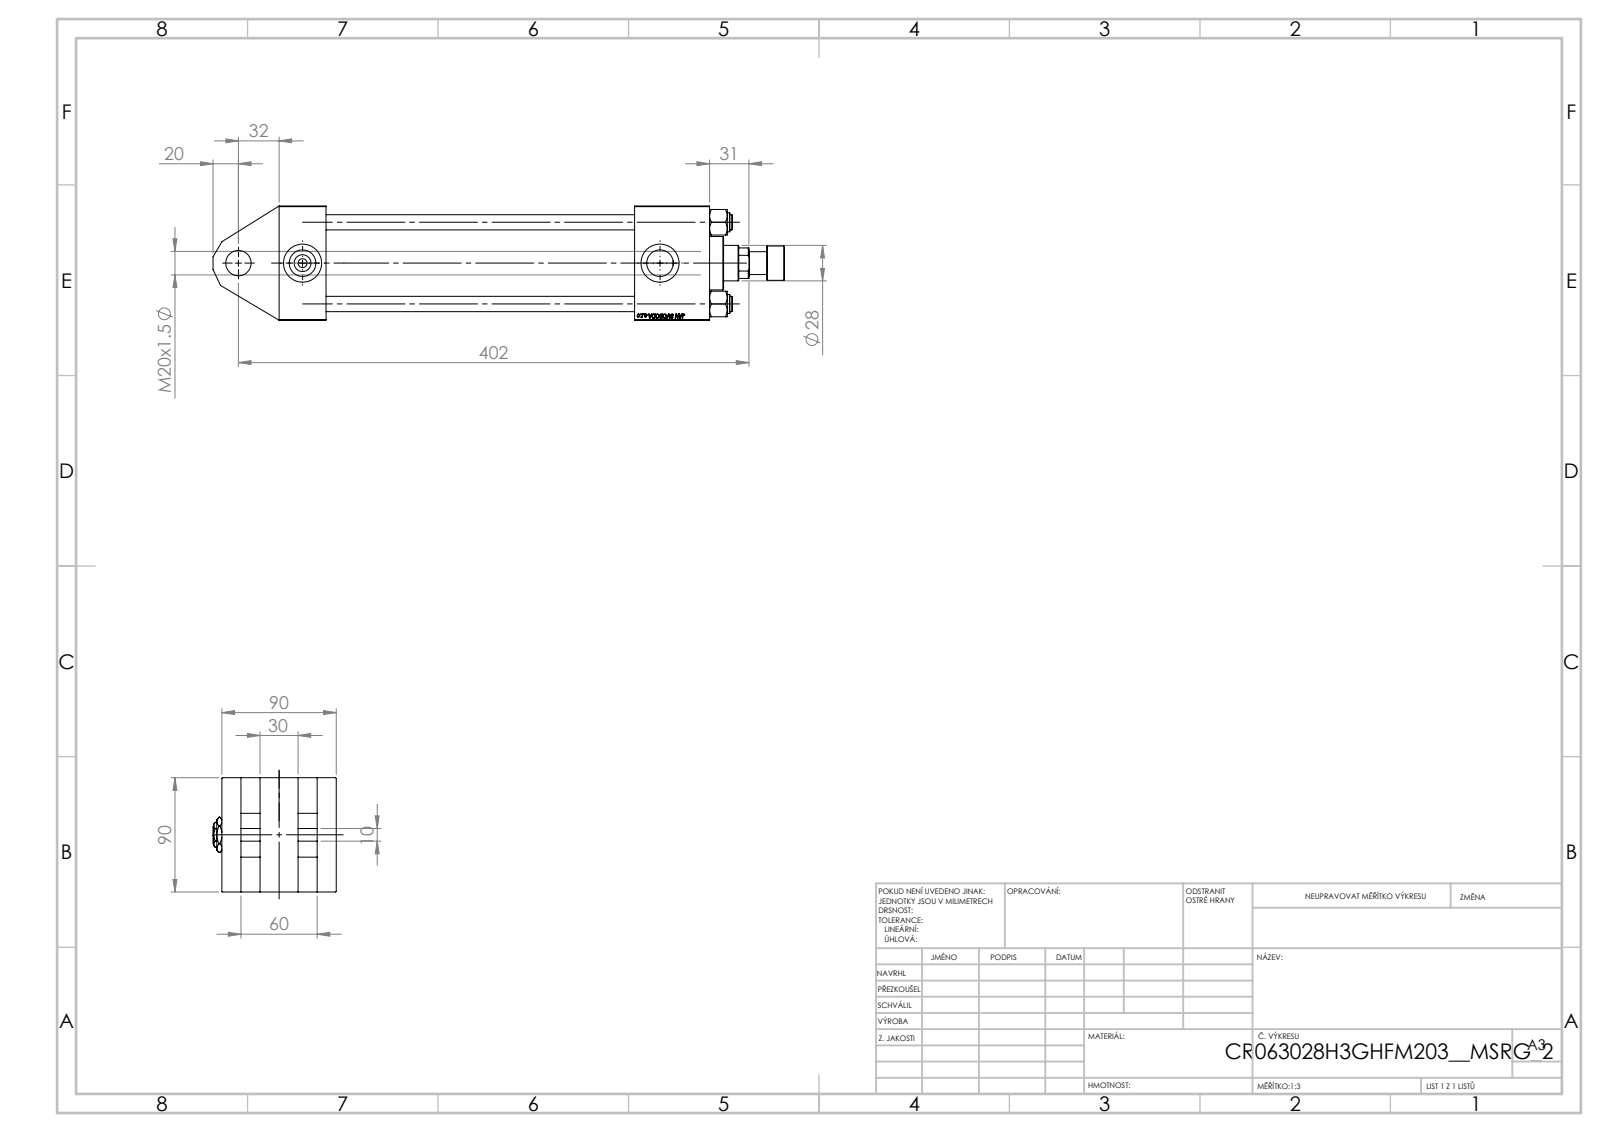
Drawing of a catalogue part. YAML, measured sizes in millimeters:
part_name: "V215_VC_A; Zatka_pro_OIL_PORT; V215CR_ROD_END_F; V215CR_VCP_H (+3 more)"
step_written_by: "SolidWorks 2019 (CONFIG_CONTROL_DESIGN)"
units: millimeters
bodies: {solids: 14, faces: 1244, planar: 570, cylindrical: 98, other: 576}
overall_size: [450, 97, 90]
volume: 1354000
surface_area: 324800
round_holes:
  - {diameter: 12, count: 4}
  - {diameter: 7, count: 2}
  - {diameter: 20.96, count: 2}
  - {diameter: 30, count: 2}
  - {diameter: 18.5, count: 1}
  - {diameter: 20, count: 1}
  - {diameter: 28, count: 1}
  - {diameter: 31, count: 1}
  - {diameter: 50, count: 1}
  - {diameter: 60, count: 1}
  - {diameter: 63, count: 1}
round_bosses_or_shafts:
  - {diameter: 15, count: 4}
  - {diameter: 69, count: 1}
  - {diameter: 42, count: 1}
  - {diameter: 27, count: 1}
  - {diameter: 18, count: 1}
face_to_face_distances: [90, 15, 60, 30, 302, 45, 37, 59, 75, 339]
hole_center_spacings: [45.47, 64.3, 90.93, 50.5, 281.5, 332]
